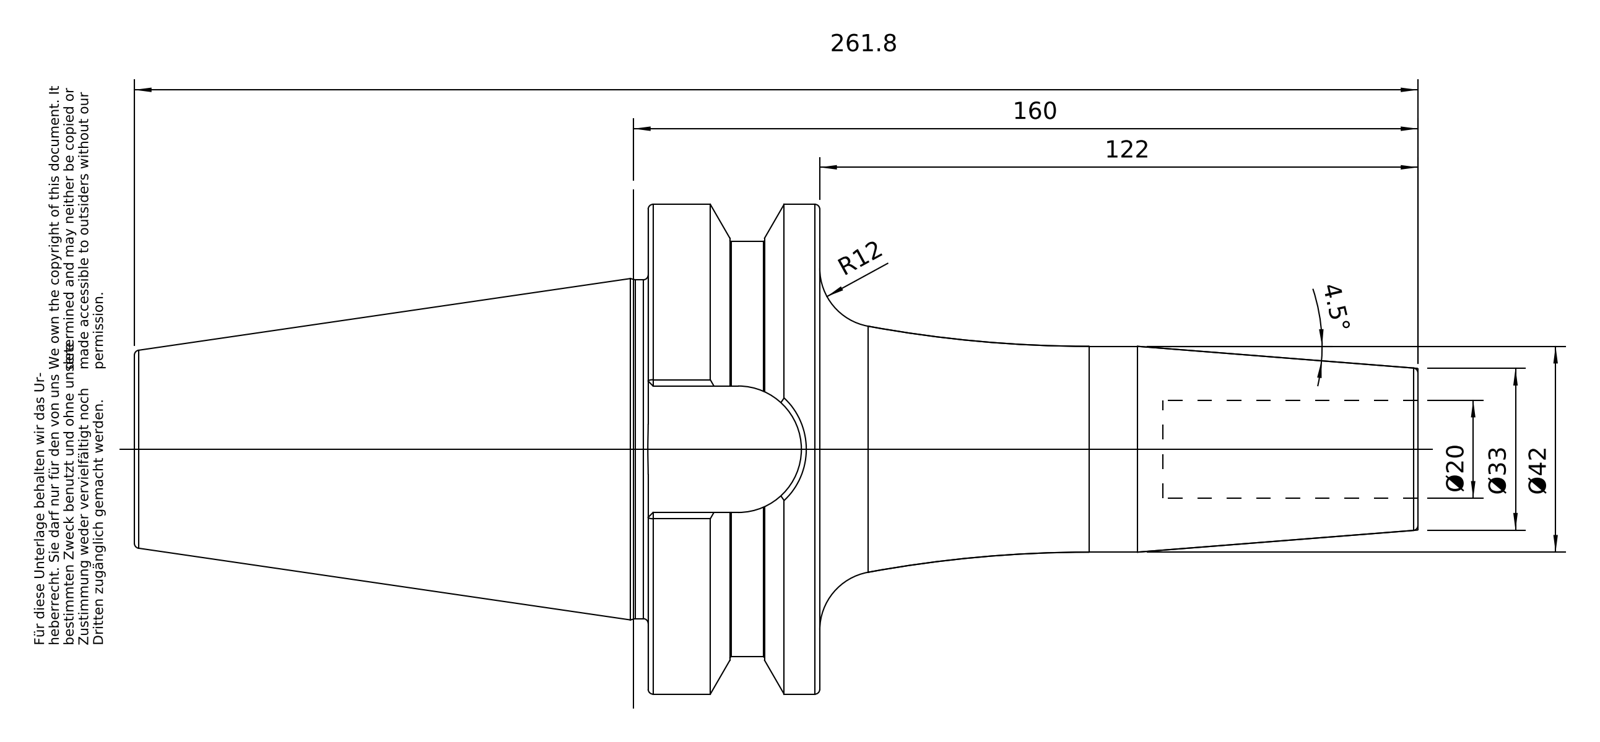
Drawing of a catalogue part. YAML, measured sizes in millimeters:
part_name: "50-642-20"
step_written_by: "PRO/ENGINEER BY PARAMETRIC TECHNOLOGY CORPORATION, 2010430 (CONFIG_CONTROL_DESIGN)"
units: millimeters
bodies: {solids: 1, faces: 98, planar: 26, cylindrical: 22, other: 50}
overall_size: [261.8, 99.97, 99.97]
volume: 624469
surface_area: 69214
round_holes:
  - {diameter: 20, count: 1}
  - {diameter: 20.75, count: 1}
  - {diameter: 25.02, count: 1}
  - {diameter: 25.7, count: 1}
round_bosses_or_shafts:
  - {diameter: 99.97, count: 1}
  - {diameter: 84.75, count: 1}
  - {diameter: 69.15, count: 1}
  - {diameter: 42, count: 1}
  - {diameter: 24.01, count: 1}
partial_cylinders:
  - {radius: 12.9, count: 1}
face_to_face_distances: [35, 70.4, 104.8, 139.8, 261.8, 157, 122, 25.8, 209.8, 105]
